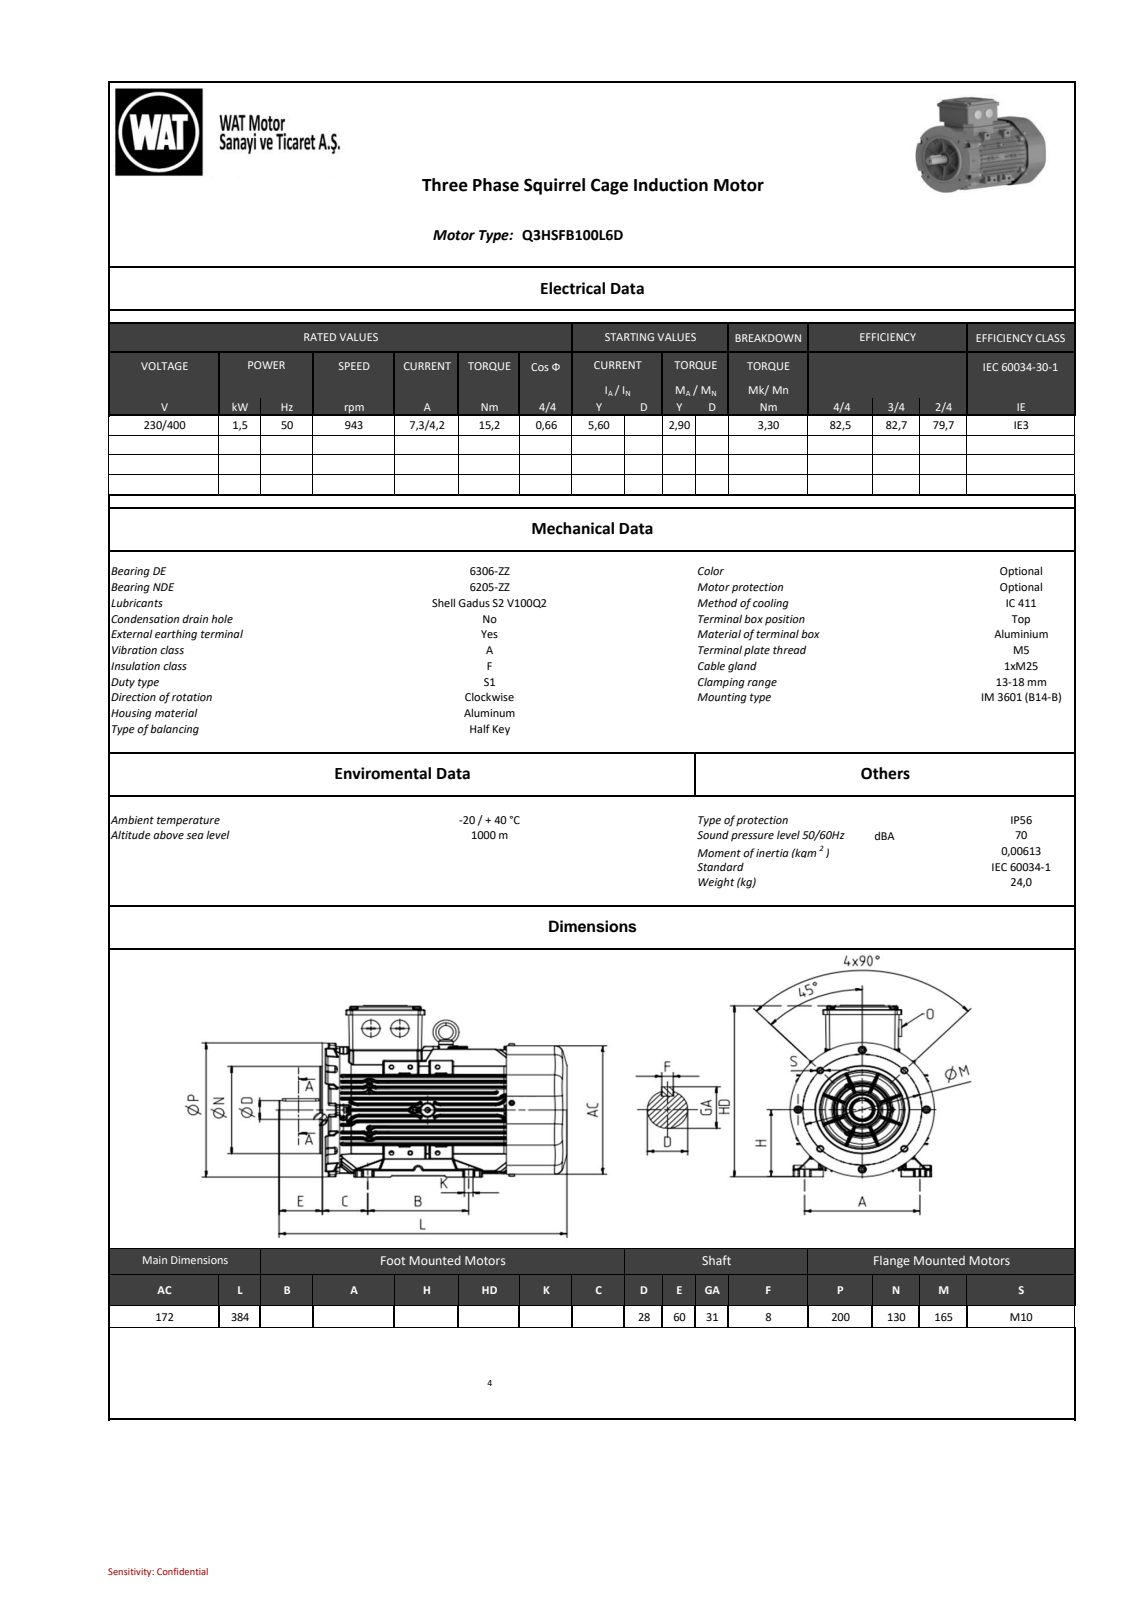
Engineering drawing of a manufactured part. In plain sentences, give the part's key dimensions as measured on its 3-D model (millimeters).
The part is named "QHS Series_100_B14b DEEP COVER_stp_objects". Its 3-D file was written by "SIEMENS PLM Software NX2206.8101 (AUTOMOTIVE_DESIGN)". It is 0 solids with 6595 faces: 1598 planar, 2792 cylindrical and 2205 other. Overall it measures 384.19 by 233.22 by 200.35 millimeters. Round holes: 4 of diameter 9, 3 of diameter 3.5, 1 of diameter 8.5, 1 of diameter 9.87, 1 of diameter 10.5, 1 of diameter 79.79, 1 of diameter 97.79, 1 of diameter 115.78. Round bosses or shafts: 7 of diameter 8, 5 of diameter 5, 4 of diameter 10, 2 of diameter 25, 1 of diameter 130, 1 of diameter 102.19, 1 of diameter 84.19, 1 of diameter 30. Partial cylindrical surfaces (rounded edges, fillets, slot ends): 704 of radius 1, 586 of radius 0.8, 296 of radius 0.5, 188 of radius 2, 72 of radius 0.7, 28 of radius 8, 10 of radius 4, 8 of radius 0.8. The main face-to-face distances are 7.5, 91.91, 8.93, 82.98, 42.5, 23.57, 50.35, 206, 7.37, 90.35. The hole center spacings are 82.51, 116.68, 39, 67.56, 82.4, 82.61, 165.01, 38.91.
